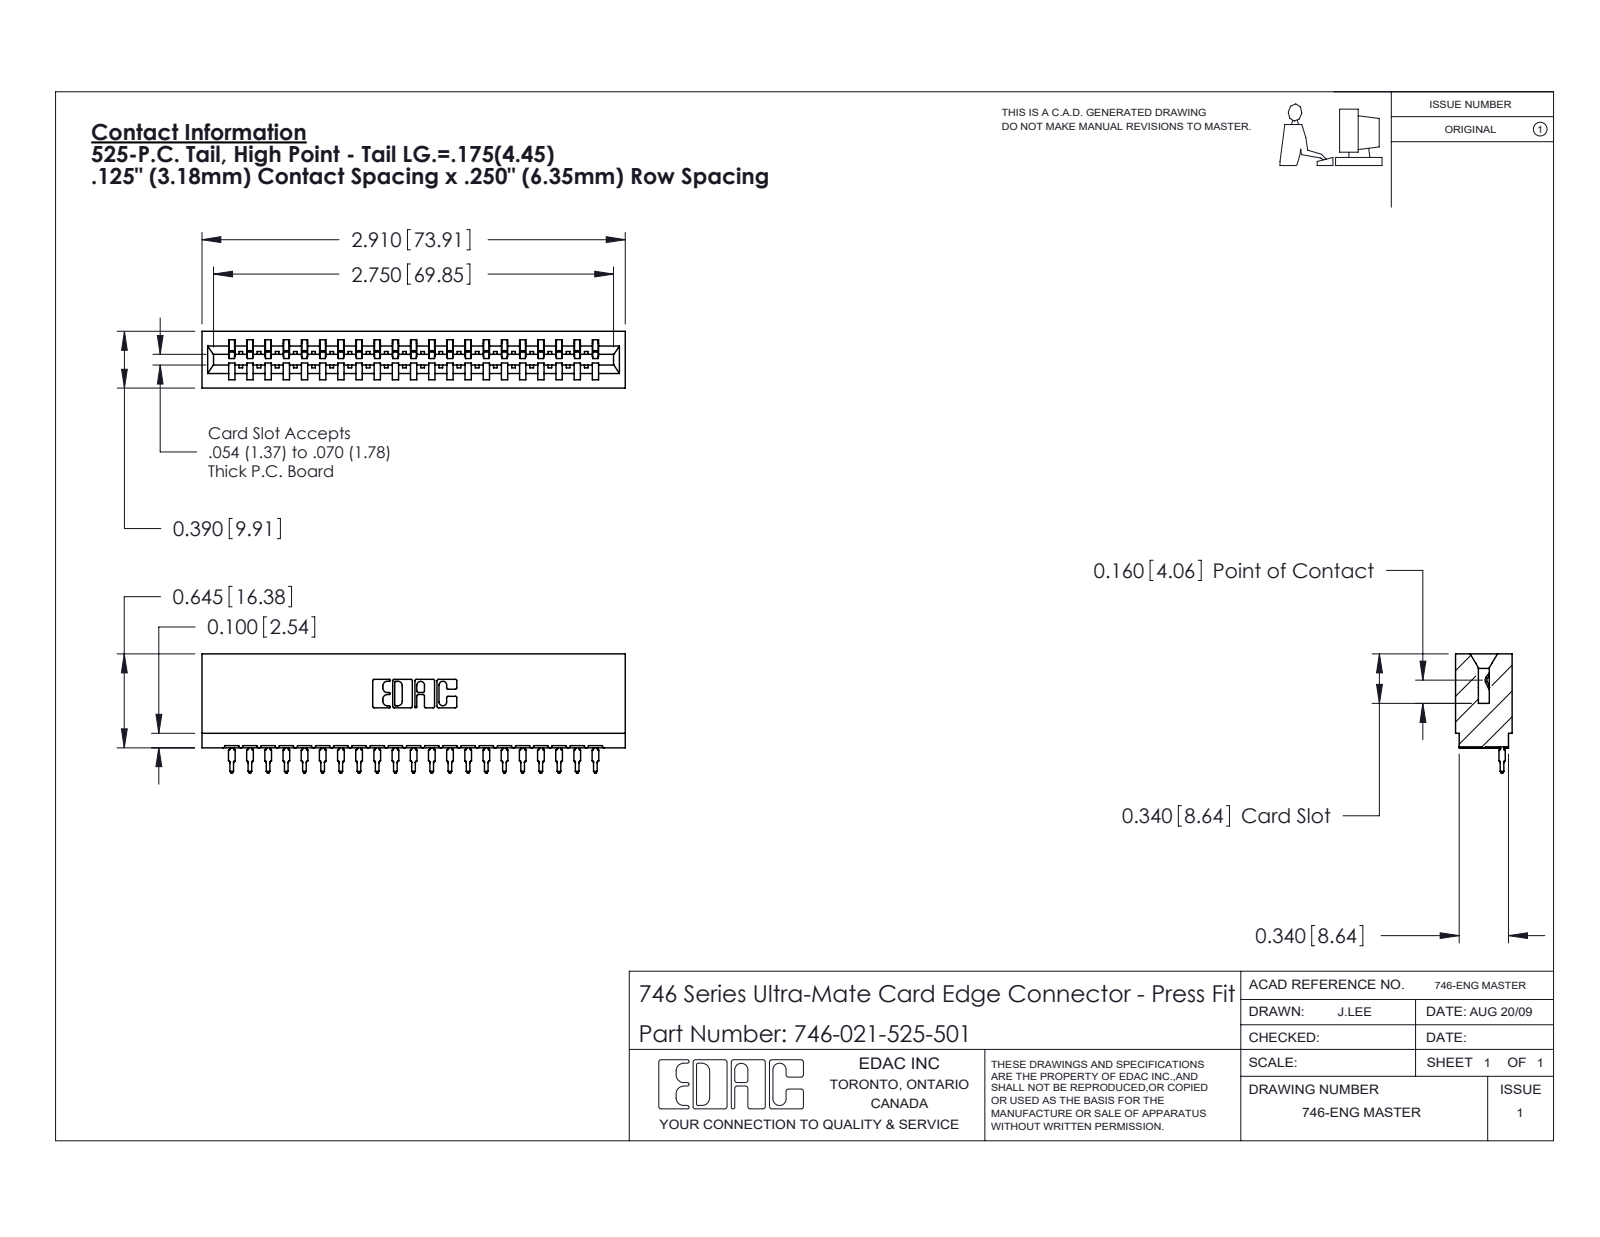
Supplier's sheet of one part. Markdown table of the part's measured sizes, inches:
| quantity | value |
| --- | --- |
| part name | 746-021-525-501; 746 Part_.340 Slot Depth - 01; 746-292-001_525 |
| STEP written by | SolidWorks 2020 (CONFIG_CONTROL_DESIGN) |
| units | inches |
| bodies | 22 solids, 2365 faces (1378 planar, 441 cylindrical, 546 other) |
| overall size | 2.91 × 0.819 × 0.39 |
| volume | 0.513 in³ |
| surface area | 16.89 in² |
| partial cylindrical surfaces (radius × count) | 0.021 × 42, 0.01 × 22, 0.015 × 22, 0.007 × 6, 0.031 × 6, 0.005 × 4, 0.011 × 4, 0.026 × 3 |
| main face-to-face distances | 0.25, 0.057, 0.333, 0.39, 0.5, 0.125, 0.292, 0.125, 0.025, 0.042 |
